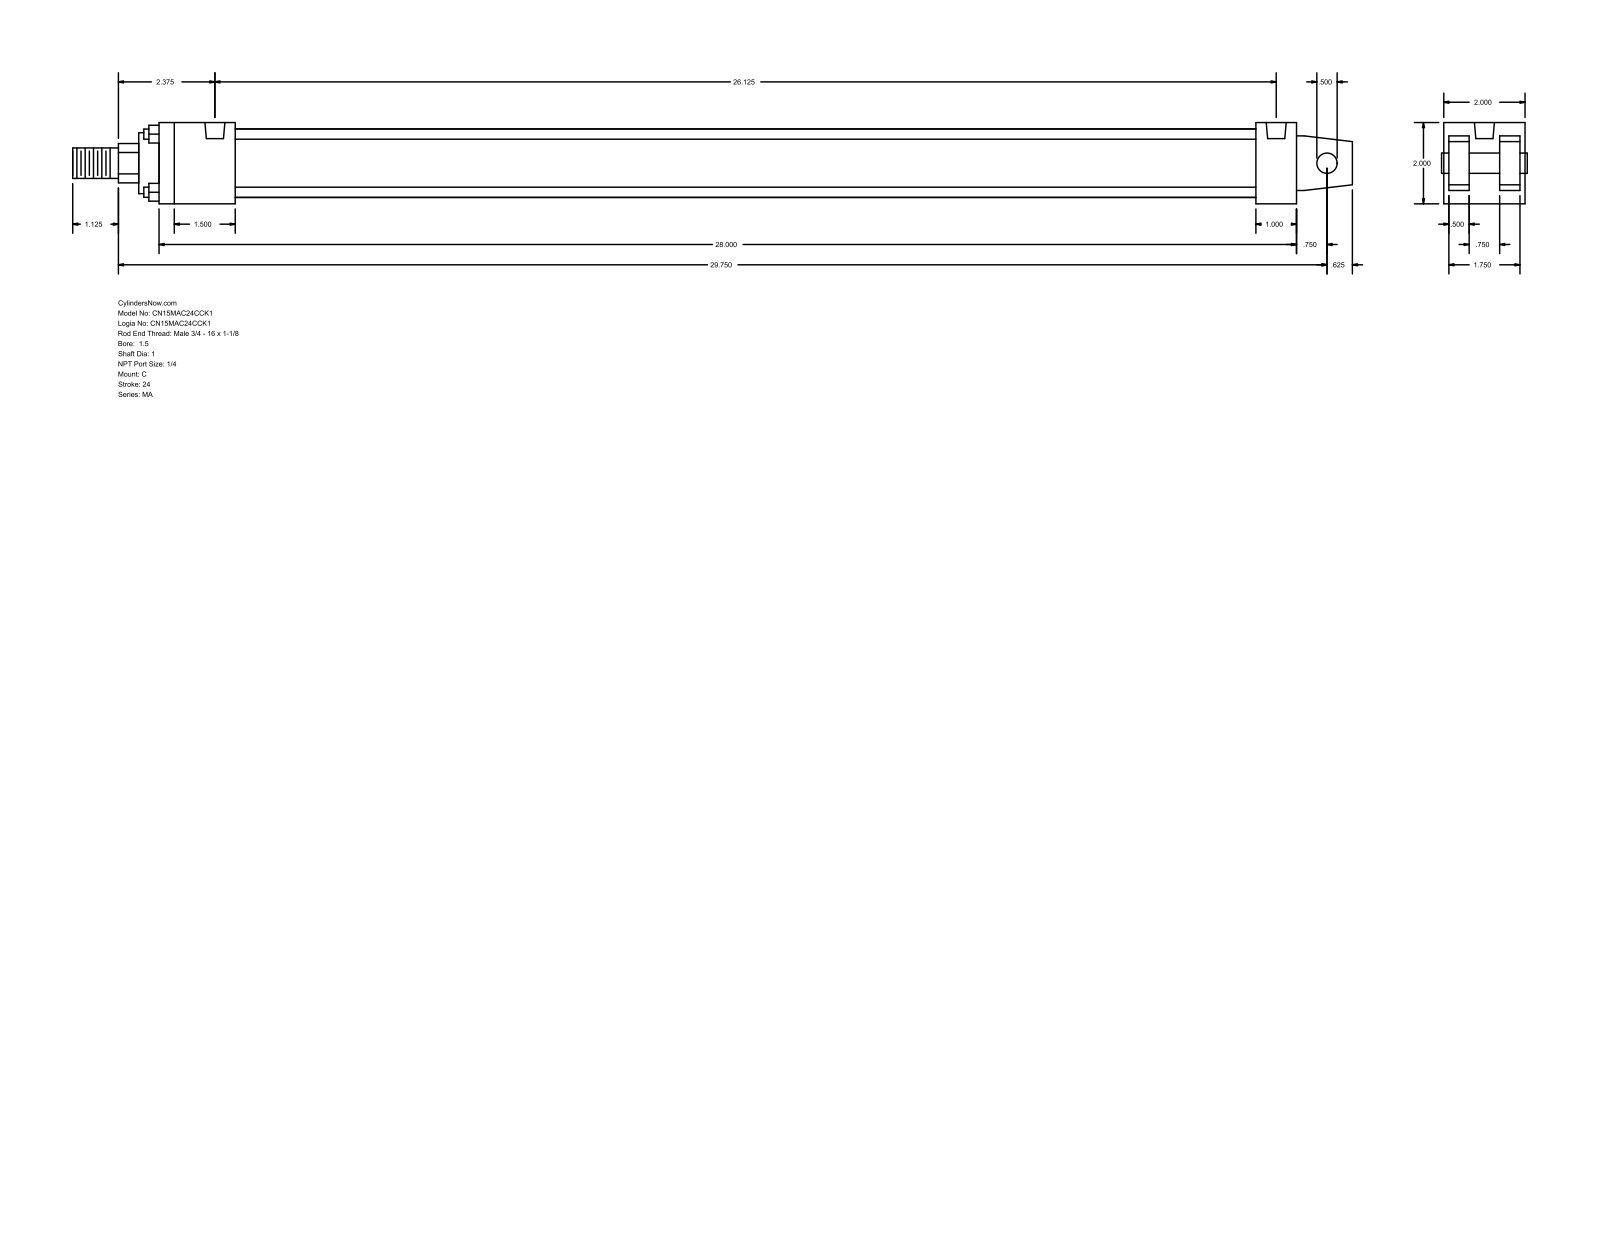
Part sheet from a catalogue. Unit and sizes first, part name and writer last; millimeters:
Units: millimetres
Overall size (bounding box): 800.1 × 50.8 × 50.8
Round holes (diameter × count): ⌀7.94 ×4, ⌀12.49 ×2
Round bosses / shafts (diameter × count): ⌀6.35 ×4, ⌀42.93 ×1, ⌀38.1 ×1, ⌀25.4 ×1, ⌀19.05 ×1, ⌀12.7 ×1
Partial cylindrical surfaces — rounded edges, fillets, slot ends (radius × count): R12.29 ×1
Main face-to-face distances: 50.8, 47.63, 12.7, 3.17, 15.87, 34.93, 31.76, 711.2, 25.4, 685.8
Hole centre spacings: 663.57
Bodies: 0 solids, 103 faces (76 planar, 27 cylindrical, 0 other)
Part name (STEP PRODUCT): MA_C__0150_1
STEP written by: GSSL Pune (CONFIG_CONTROL_DESIGN)
